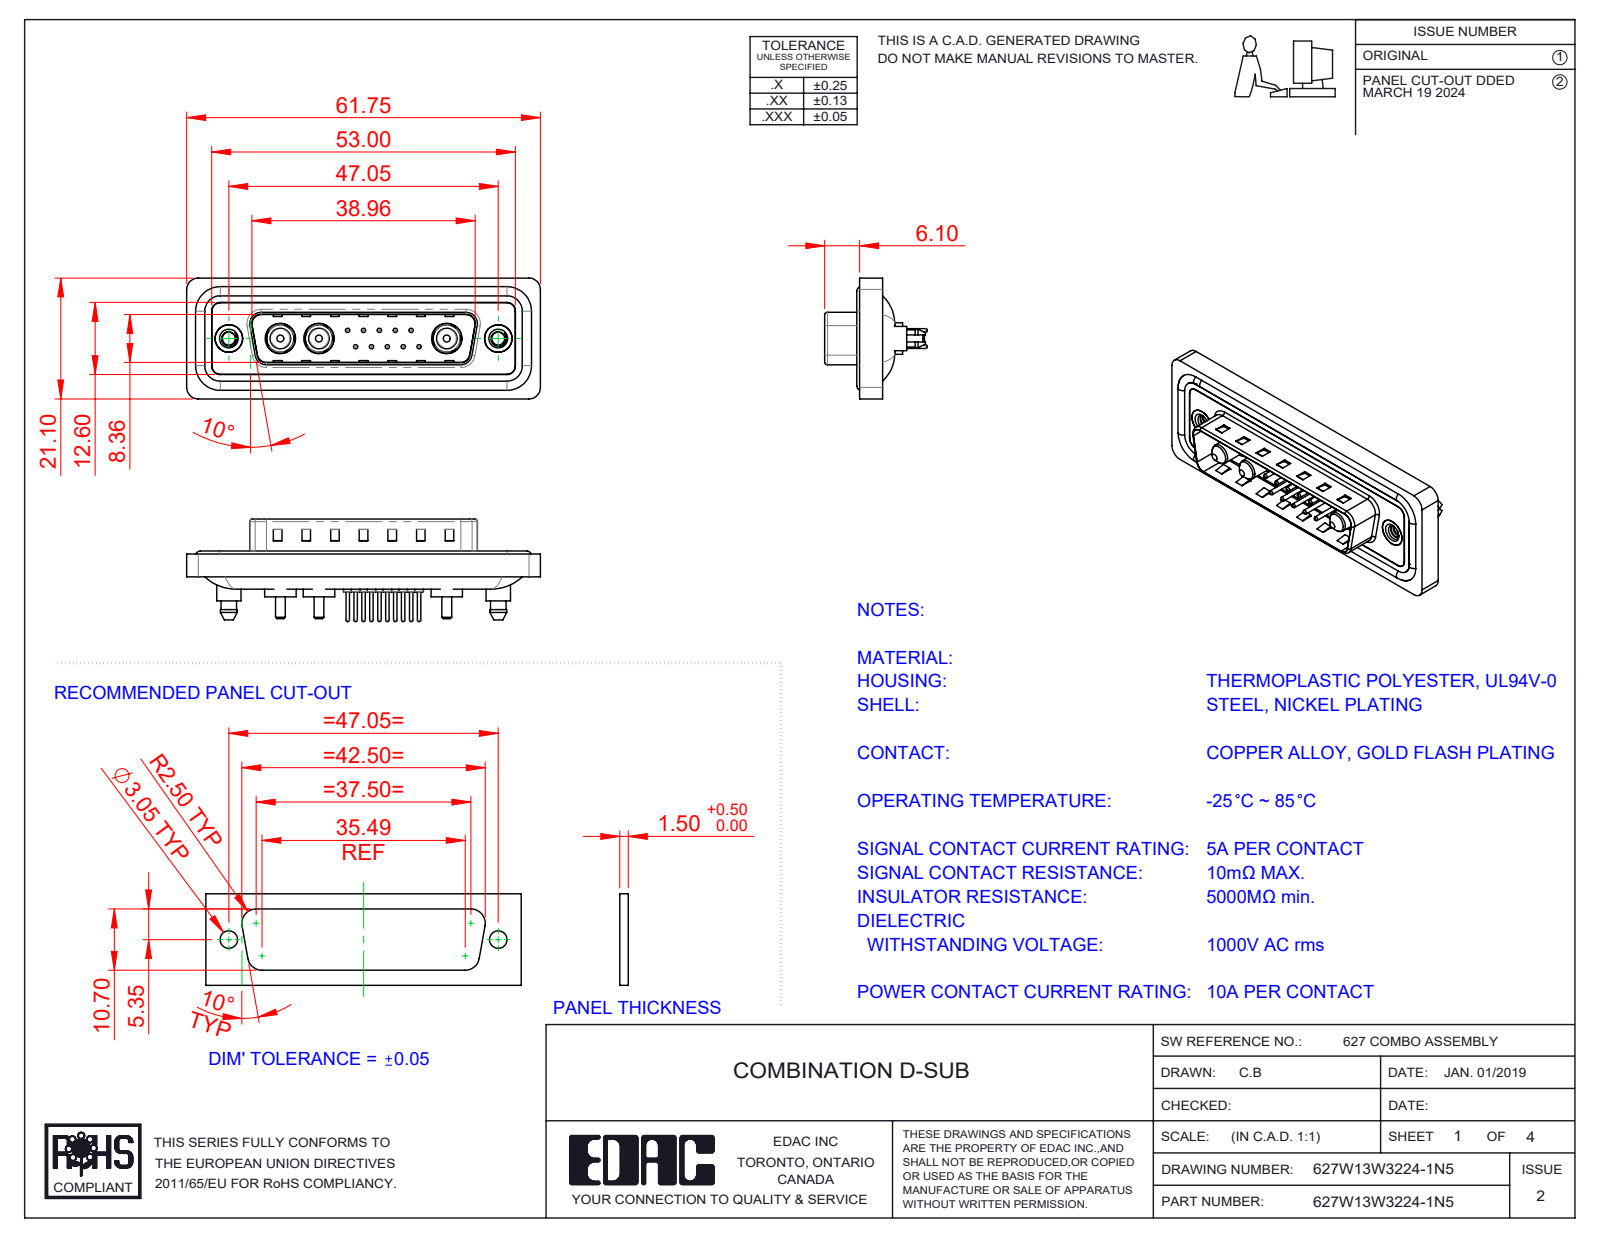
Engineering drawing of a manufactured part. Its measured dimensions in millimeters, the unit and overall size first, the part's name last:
Units: millimetres
Overall size (bounding box): 61.75 × 21.1 × 17.9
Round holes (diameter × count): ⌀0.75 ×10, ⌀1.6 ×10, ⌀2 ×10, ⌀4.85 ×3, ⌀5.3 ×3, ⌀2.26 ×2, ⌀4 ×2, ⌀4.8 ×2, ⌀5 ×2
Round bosses / shafts (diameter × count): ⌀1.5 ×10, ⌀0.6 ×10, ⌀1.6 ×4, ⌀5.5 ×3, ⌀5.2 ×3, ⌀4.75 ×3, ⌀3.75 ×3, ⌀3.6 ×3
Partial cylindrical surfaces — rounded edges, fillets, slot ends (radius × count): R1.5 ×24, R2 ×18, R1.6 ×10, R0.5 ×8, R0.25 ×4, R0.6 ×4, R0.65 ×4, R0.9 ×4
Main face-to-face distances: 0.4, 1.5, 1.1, 1.6, 0.5, 3.1, 2.9, 0.82, 9.58, 4.1
Hole centre spacings: 3.16, 2.77, 5.04, 5.54, 7.49, 5.03, 8.31, 10.11
Volume: 7 425 mm³ · Surface area: 12 170 mm²
Bodies: 23 solids, 1020 faces (325 planar, 417 cylindrical, 278 other)
Part name (STEP PRODUCT): 627Combo Housing_13W3; 627Combo Shell Front_25 Contacts; 627Combo Waterproof Housing_25 Contacts; 627Combo Threaded Boardlock_5 (+5 more)
STEP written by: SolidWorks 2023 (CONFIG_CONTROL_DESIGN)
